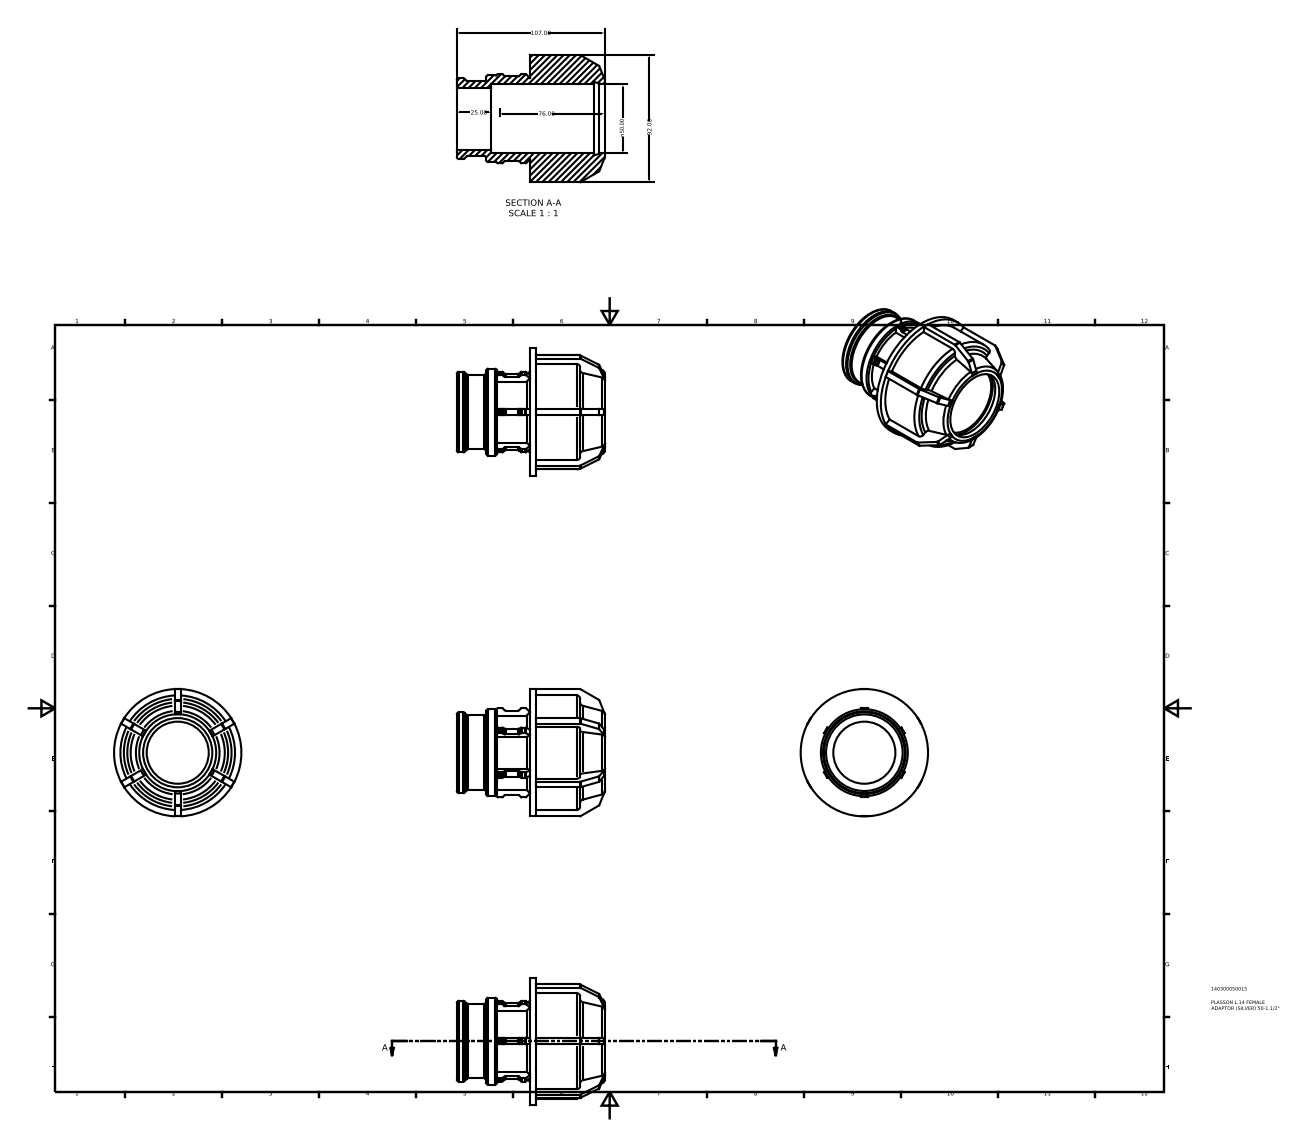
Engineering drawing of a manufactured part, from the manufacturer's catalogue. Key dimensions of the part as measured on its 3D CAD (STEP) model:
Part name (STEP PRODUCT): 140300050015
STEP written by: Autodesk Inventor 2015 (AUTOMOTIVE_DESIGN)
Units: millimetres
Bodies: 1 solid, 260 faces (159 planar, 67 cylindrical, 34 other)
Overall size (bounding box): 107 × 92 × 92
Volume: 197 019 mm³ · Surface area: 54 092 mm²
Round holes (diameter × count): ⌀44.84 ×1, ⌀50 ×1
Round bosses / shafts (diameter × count): ⌀92 ×1, ⌀82.8 ×1, ⌀62.78 ×1, ⌀58.3 ×1, ⌀53.81 ×1
Partial cylindrical surfaces — rounded edges, fillets, slot ends (radius × count): R1.5 ×48
Main face-to-face distances: 4.6, 4.1, 52.88, 56.98, 3.75, 50.02, 28.75, 24.13, 28.23, 89.14
